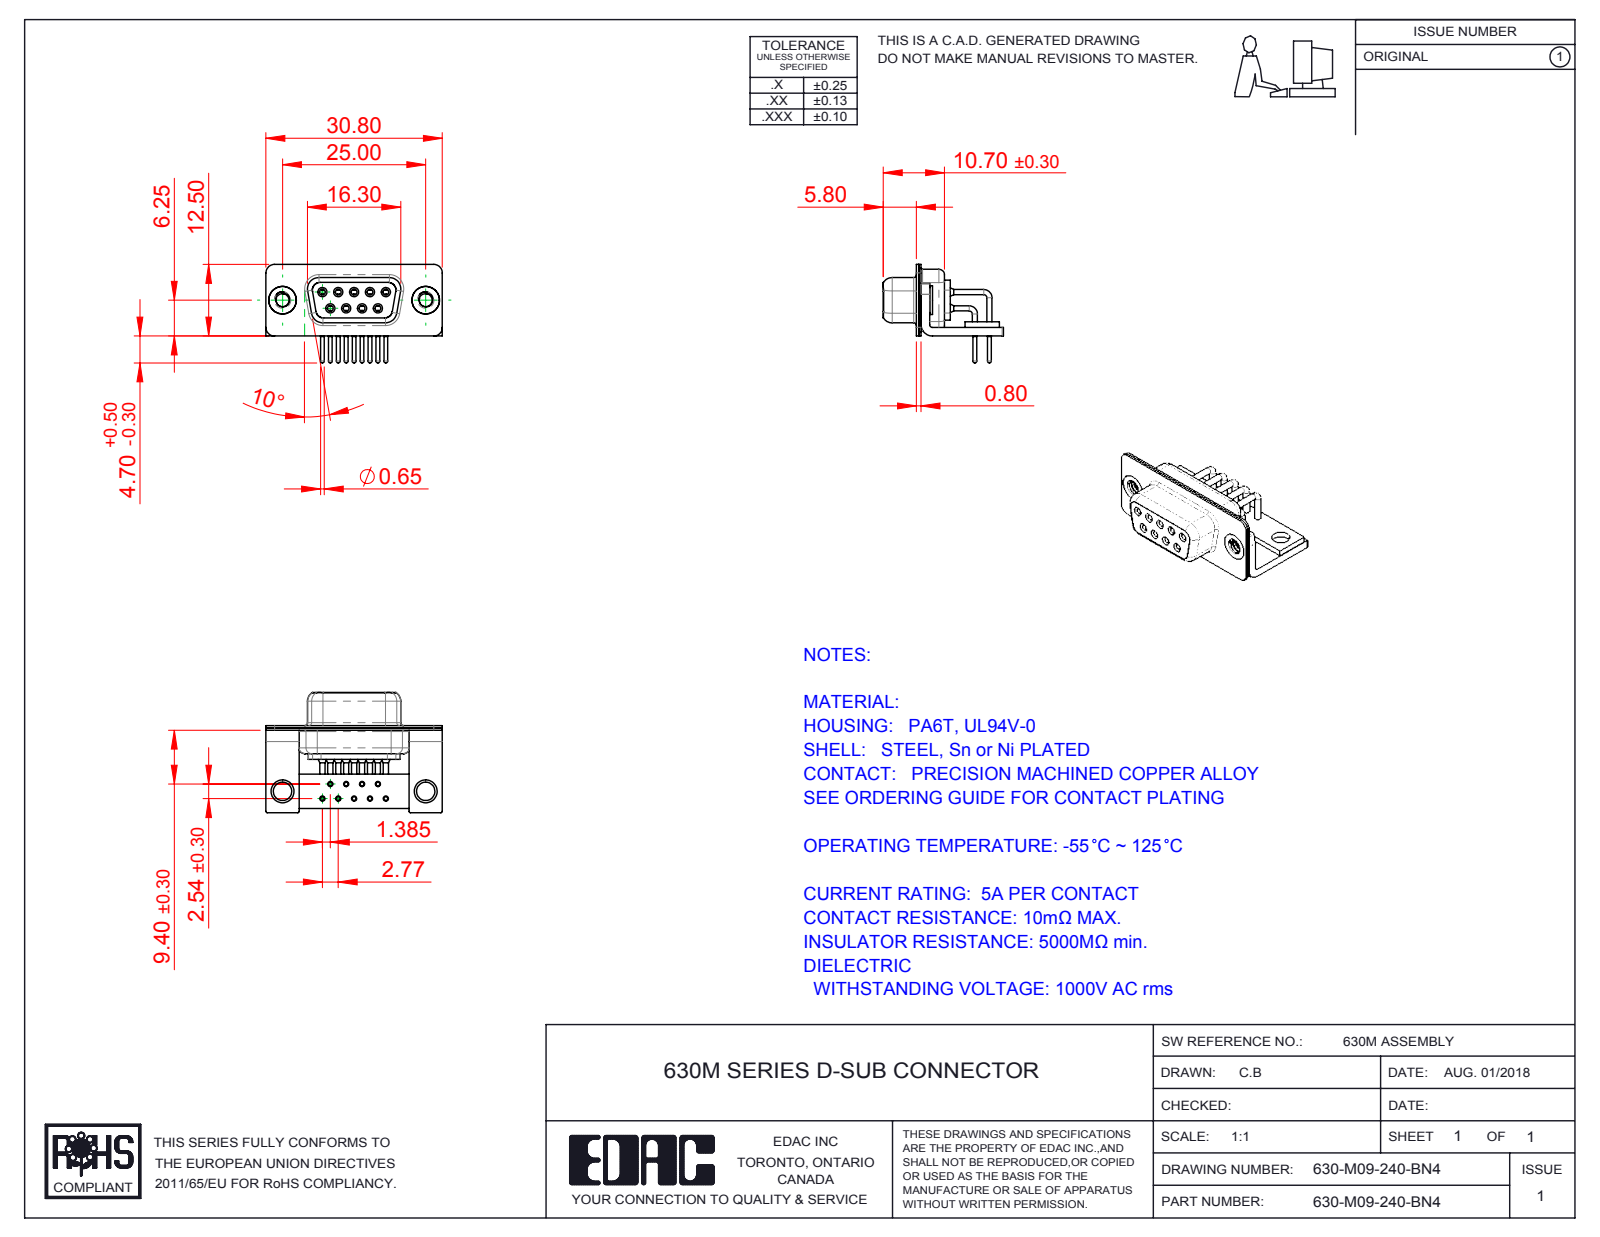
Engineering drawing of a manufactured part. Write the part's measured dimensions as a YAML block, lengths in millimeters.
part_name: "630M Shell Front_09 Contacts; 630M Housing_09 Contacts; 630M Shell Rear_09 Contacts; 630M Contact Row 2 (+5 more)"
step_written_by: "SolidWorks 2016 (CONFIG_CONTROL_DESIGN)"
units: millimeters
bodies: {solids: 17, faces: 824, planar: 228, cylindrical: 384, other: 212}
overall_size: [30.8, 21, 17.2]
volume: 2191
surface_area: 5674
round_holes:
  - {diameter: 0.9, count: 9}
  - {diameter: 1, count: 9}
  - {diameter: 1.1, count: 9}
  - {diameter: 1.7, count: 9}
  - {diameter: 1.8, count: 9}
  - {diameter: 2, count: 9}
  - {diameter: 2.26, count: 2}
  - {diameter: 3.2, count: 2}
  - {diameter: 4, count: 2}
  - {diameter: 4.8, count: 2}
round_bosses_or_shafts:
  - {diameter: 1.6, count: 9}
  - {diameter: 1.5, count: 9}
  - {diameter: 0.9, count: 9}
  - {diameter: 0.65, count: 9}
  - {diameter: 5, count: 2}
  - {diameter: 4.9, count: 2}
partial_cylinders:
  - {radius: 0.25, count: 16}
  - {radius: 1.5, count: 16}
  - {radius: 2, count: 13}
  - {radius: 1.35, count: 8}
  - {radius: 1.6, count: 8}
  - {radius: 0.5, count: 5}
  - {radius: 0.6, count: 4}
  - {radius: 0.65, count: 4}
face_to_face_distances: [0.4, 0.8, 1.5, 2.3, 1.9, 1, 9.35, 1.45, 2.5, 8.95]
hole_center_spacings: [2.77, 5.54, 3.16, 4.87, 8.31, 2.89, 2.9, 5.03]
